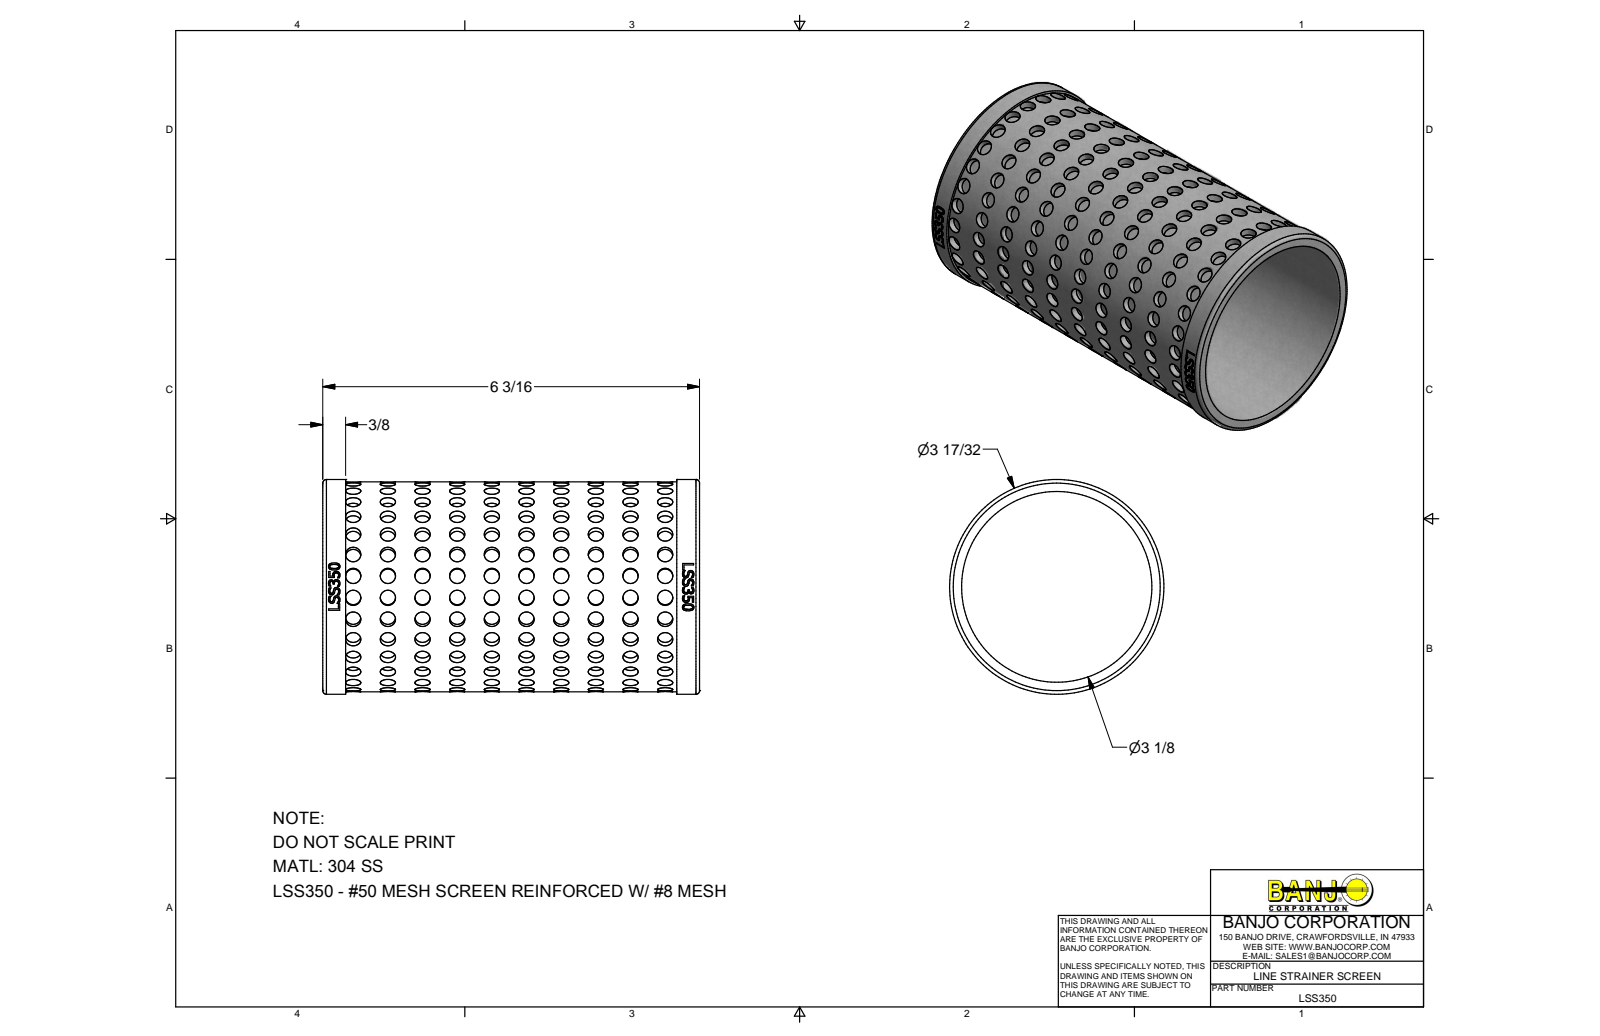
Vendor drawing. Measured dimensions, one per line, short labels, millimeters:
name: LSS350
written by: Autodesk Inventor 2013 (AUTOMOTIVE_DESIGN)
unit: mm
bodies: 1 solid, 834 faces (362 planar, 318 cylindrical, 154 other)
size: 157.2 × 89.4 × 89.4
volume: 141 800 mm³; area: 103 000 mm²
holes: 250× ⌀6.4, 1× ⌀79.4
bosses: 1× ⌀89.4, 1× ⌀87.4
rounds: 1× R44.2
face distances: 81.4, 81.4, 157.2, 81.4, 147.7, 9.5, 138.2, 2.5, 7.1, 31
hole spacings: 28.9, 14.5, 43.4, 72.3, 14.5, 57.9, 101.2, 43.4
